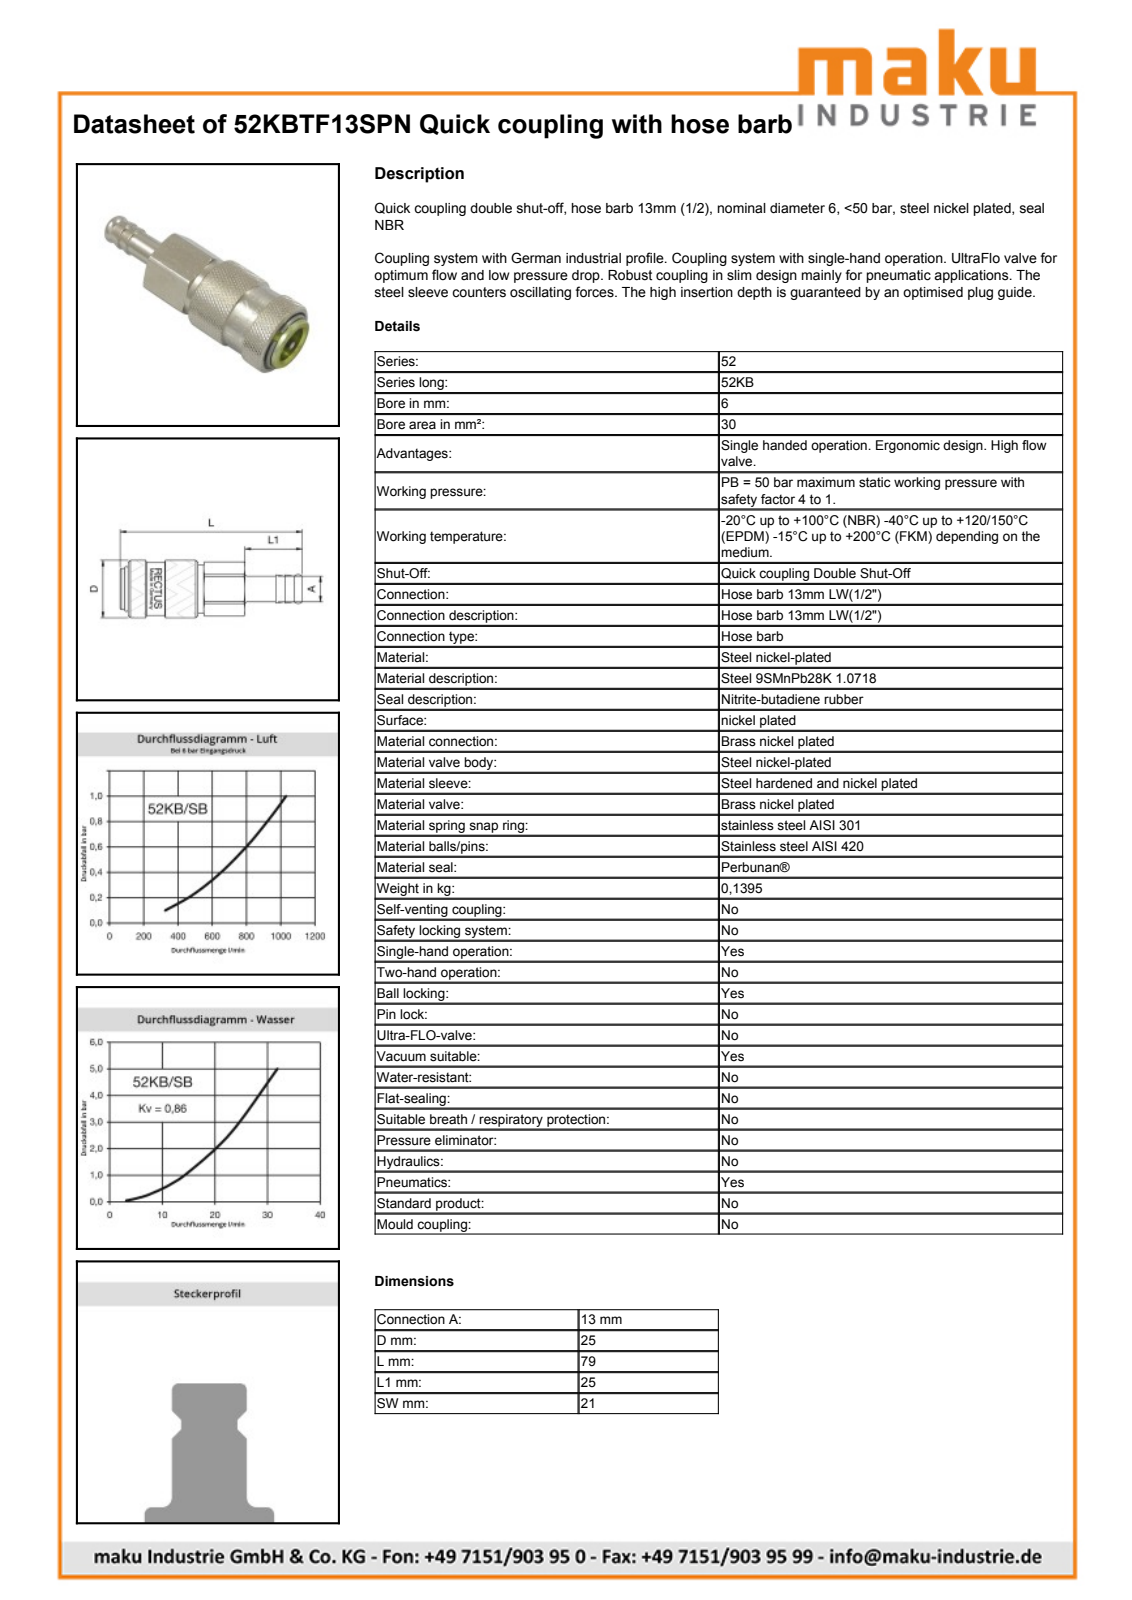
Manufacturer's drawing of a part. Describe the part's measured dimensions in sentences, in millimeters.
The part is named "D106544". Its 3-D file was written by "Autodesk Inventor 2011 (AUTOMOTIVE_DESIGN)". It is 3 solids with 523 faces: 198 planar, 63 cylindrical and 262 other. Overall it measures 79.55 by 25.15 by 25.15 millimeters. Its volume is 25 059 cubic millimeters and its surface area 11 337 square millimeters. Round holes: 1 of diameter 11, 1 of diameter 15.35, 1 of diameter 17, 1 of diameter 18.25, 1 of diameter 20.5, 1 of diameter 21. Round bosses or shafts: 1 of diameter 25.15, 1 of diameter 23, 1 of diameter 20.85, 1 of diameter 18, 1 of diameter 16.65, 1 of diameter 16.5, 1 of diameter 14.44, 1 of diameter 13.2. Partial cylindrical surfaces (rounded edges, fillets, slot ends): 1 of radius 11.4, 1 of radius 11.85. The main face-to-face distances are 21, 54.55, 3.5, 3.32, 24.99, 79.54, 25, 72.72, 47.73, 6.82.
